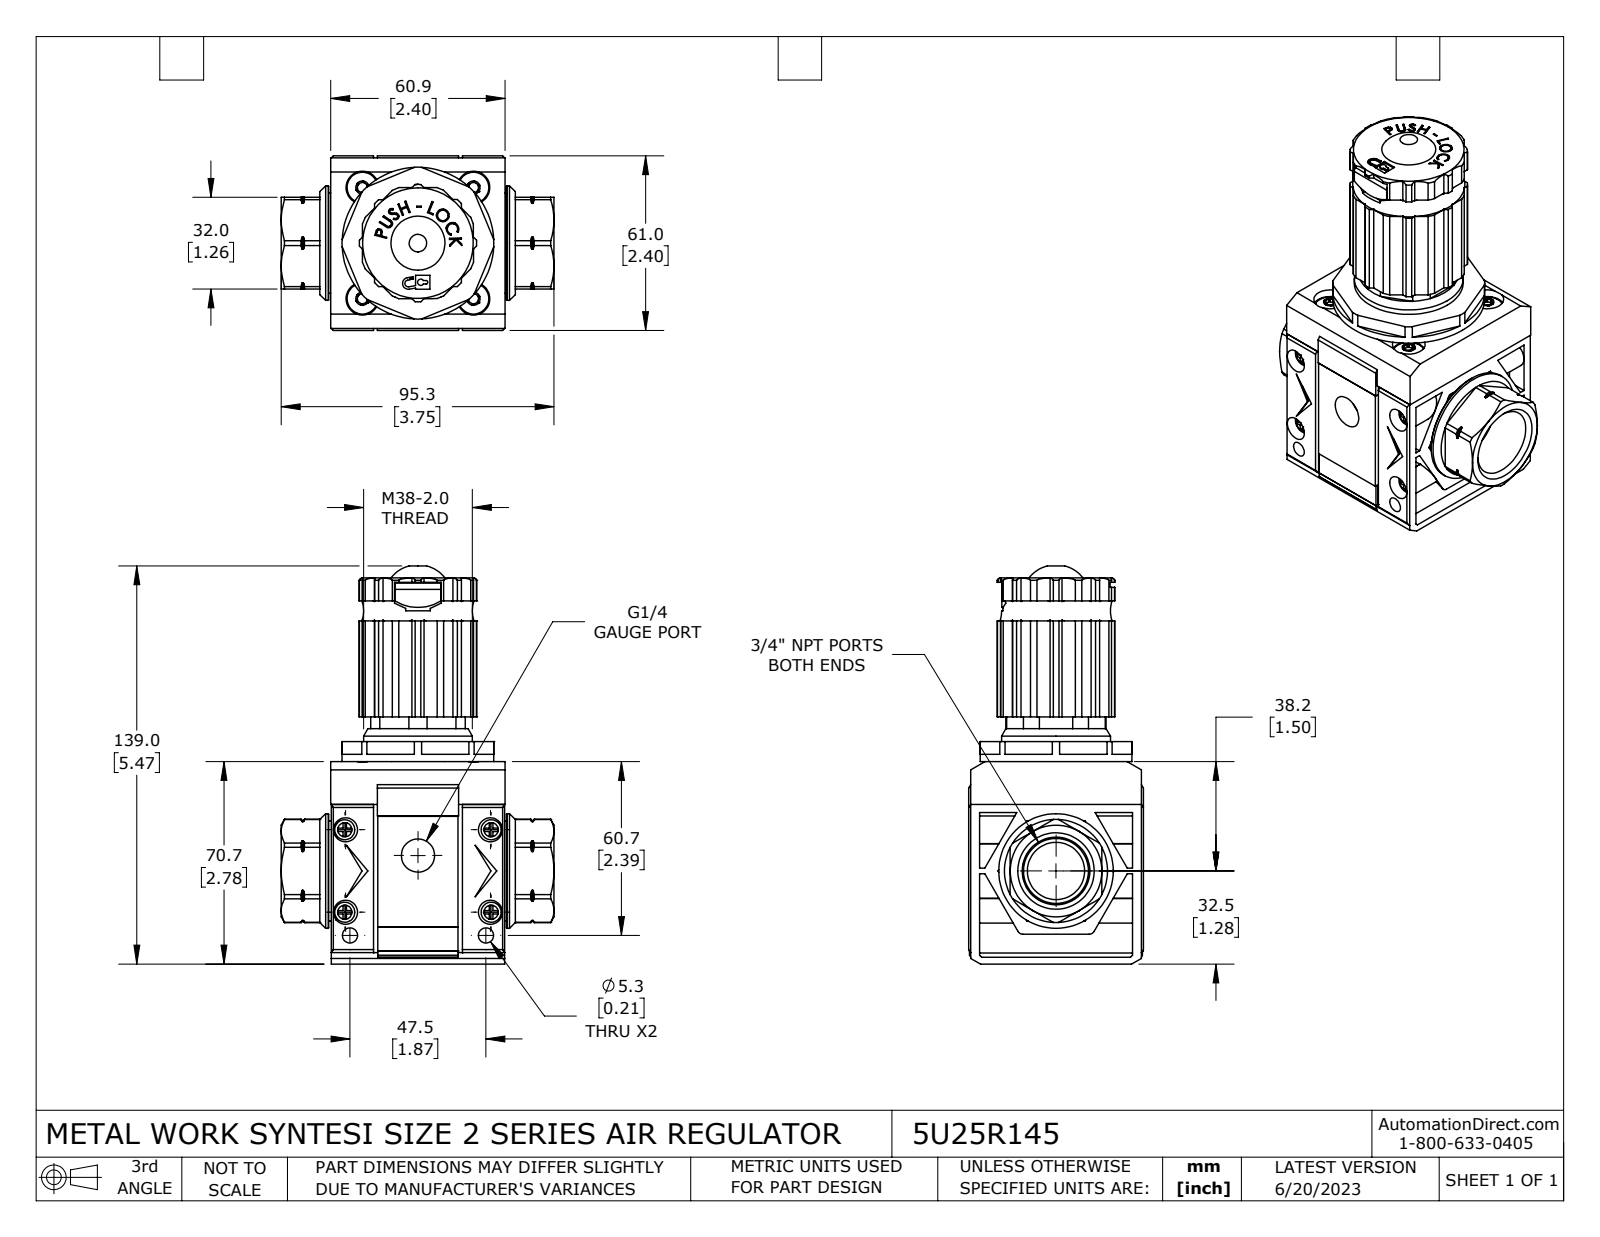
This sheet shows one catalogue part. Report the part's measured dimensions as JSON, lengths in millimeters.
{"part_name": "5U25R145", "step_written_by": "SolidWorks 2021 (CONFIG_CONTROL_DESIGN)", "units": "millimeters", "bodies": {"solids": 12, "faces": 1198, "planar": 621, "cylindrical": 377, "other": 200}, "overall_size": [139, 95.3, 61], "volume_mm3": 212400, "surface_area_mm2": 89350, "round_holes": [[3.3, 4], [4.2, 4], [8.4, 4], [11.4, 4], [5.3, 2], [11.6, 1], [20, 1], [31.8, 1], [35.8, 1], [38.3, 1]], "round_bosses_or_shafts": [[7, 4], [4.8, 4], [3.8, 4], [53, 1], [40, 1], [38, 1], [35, 1], [31.7, 1]], "partial_cylinders_radius": [[0.3, 28], [1.8, 4], [4.9, 4], [20.5, 4], [2, 2], [6.1, 2], [0.6, 1], [0.6, 1]], "face_to_face_distances": [60.7, 2.4, 55.7, 53.3, 15, 70.7, 68.3, 0.7, 61, 7.6], "hole_center_spacings": [27.4, 38.8, 8.3, 26.8, 28.8, 32.1, 36.7, 36.9]}
